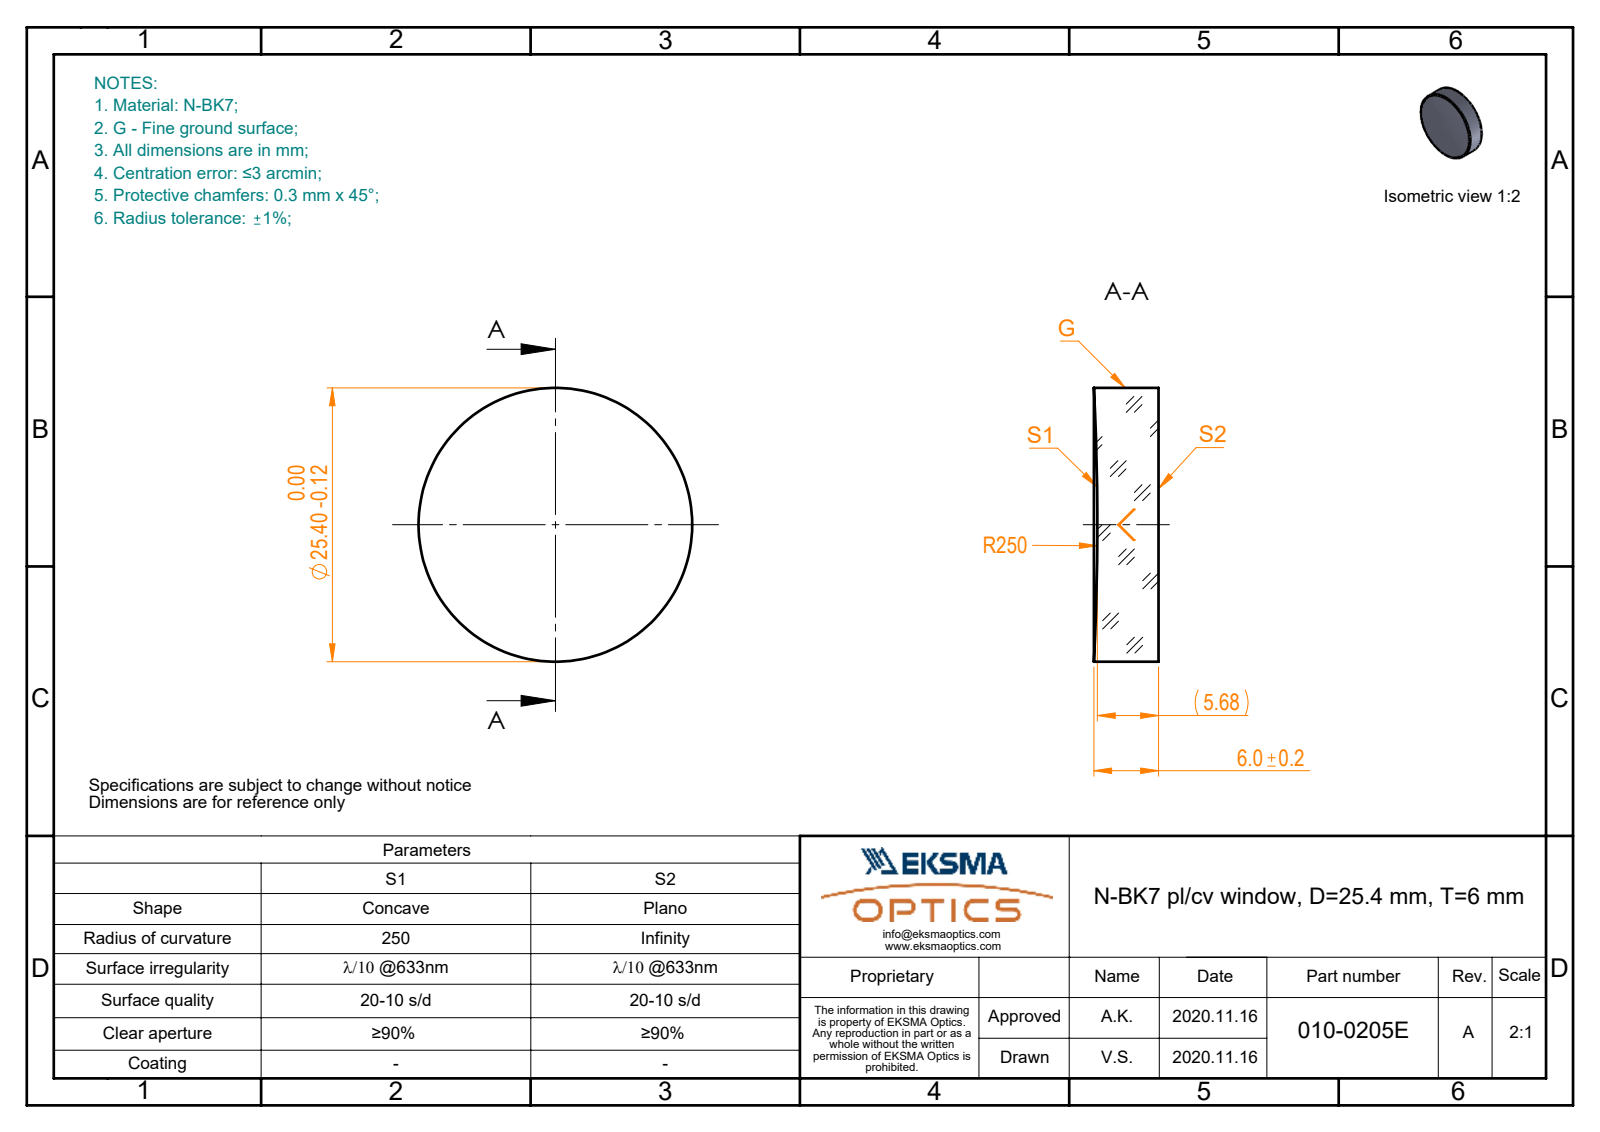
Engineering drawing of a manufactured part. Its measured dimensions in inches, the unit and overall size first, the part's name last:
Units: inches
Overall size (bounding box): 1 × 1 × 0.236
Round bosses / shafts (diameter × count): ⌀1 ×1
Volume: 0.181 in³ · Surface area: 2.314 in²
Bodies: 1 solid, 5 faces (1 planar, 2 cylindrical, 2 other)
Part name (STEP PRODUCT): 010-0205E_N-BK7_PCV_window
STEP written by: SolidWorks 2019 (CONFIG_CONTROL_DESIGN)
